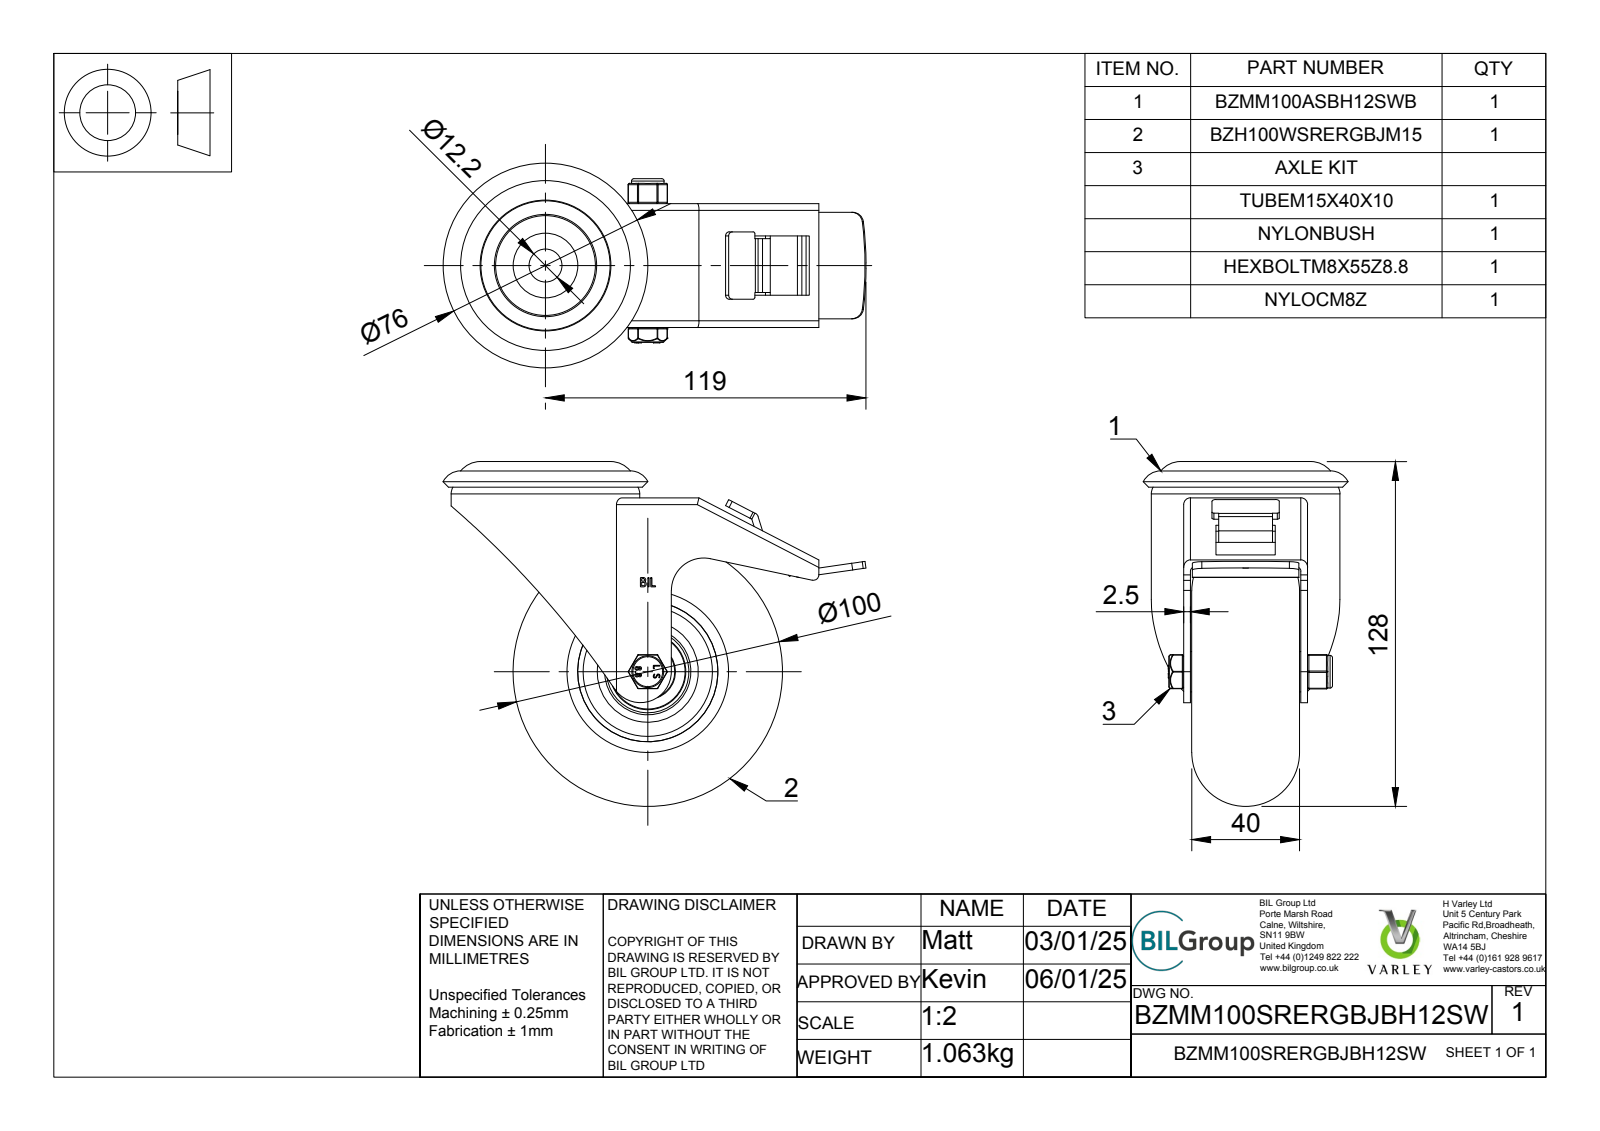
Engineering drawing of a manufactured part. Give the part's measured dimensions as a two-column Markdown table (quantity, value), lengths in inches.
| quantity | value |
| --- | --- |
| part name | BZMM100ASBH12SWB; PRESSED STEEL, ZINC PLATED HEAD; PRESSED STEEL, ZINC PLATED FORKS; PRESSED STEEL, ZINC PLATED BRAKE PEDAL (+8 more) |
| STEP written by | Spatial InterOp 3D (AUTOMOTIVE_DESIGN) |
| units | inches |
| bodies | 40 solids, 1618 faces (522 planar, 447 cylindrical, 649 other) |
| overall size | 6.181 × 5.039 × 2.992 |
| volume | 19.61 in³ |
| surface area | 198.9 in² |
| round holes (diameter × count) | 0.026 × 2, 0.315 × 1, 0.323 × 1, 0.339 × 1, 0.402 × 1, 0.48 × 1, 0.591 × 1, 0.807 × 1, 1.024 × 1, 1.055 × 1, 1.102 × 1, 1.11 × 1 |
| round bosses / shafts (diameter × count) | 2.756 × 1, 1.949 × 1, 1.496 × 1, 1.476 × 1, 0.945 × 1, 0.846 × 1, 0.839 × 1, 0.787 × 1 |
| partial cylindrical surfaces (radius × count) | 0.03 × 50, 0.02 × 18, 0.01 × 12, 0.049 × 10, 0.013 × 4, 0.025 × 4, 0.098 × 4, 0.079 × 3 |
| main face-to-face distances | 0.098, 1.673, 1.575, 1.22, 1.772, 0.354, 0.256, 0.039, 0.118, 0.339 |
| hole center spacings | 0.098, 0.126, 0.127 |
